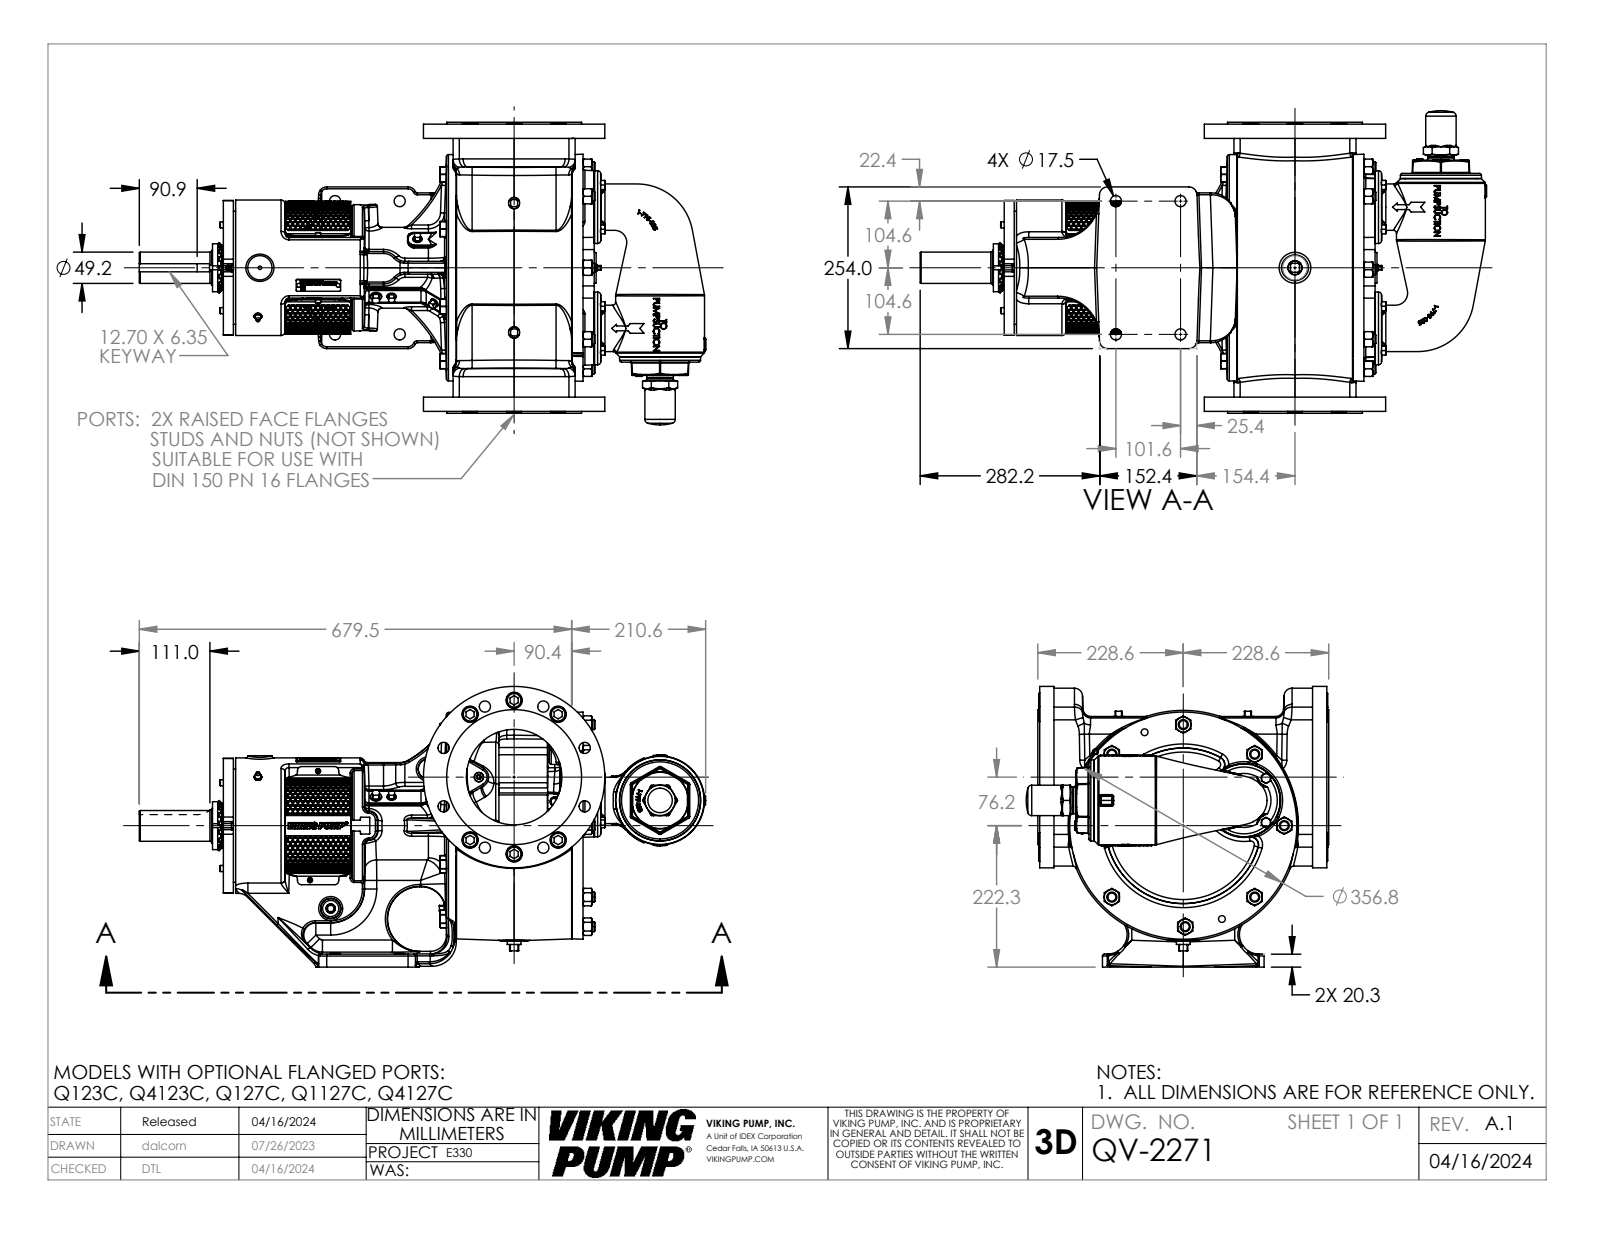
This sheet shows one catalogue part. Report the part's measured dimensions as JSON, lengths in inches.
{"part_name": "QV-2271", "step_written_by": "SolidWorks 2022 (AUTOMOTIVE_DESIGN)", "units": "inches", "bodies": {"solids": 1, "faces": 8750, "planar": 3183, "cylindrical": 833, "other": 4734}, "overall_size": [35.042, 18.719, 17.36], "volume_in3": 2561, "surface_area_in2": 2459, "round_holes": [[0.266, 8], [0.406, 8], [0.689, 8], [1.157, 8], [0.25, 6], [0.656, 6], [1, 6], [0.688, 4], [0.159, 2], [0.313, 2], [0.33, 2], [0.213, 1]], "round_bosses_or_shafts": [[0.375, 10], [0.617, 8], [0.937, 6], [0.625, 4], [0.437, 3], [0.312, 3], [4.5, 2], [0.625, 2]], "partial_cylinders_radius": [[0.12, 60], [0.06, 30], [0.25, 30], [0.5, 23], [0.015, 18], [0.092, 18], [0.75, 14], [0.03, 12]], "face_to_face_distances": [1, 17, 18, 16, 3.75, 0.5, 21.756, 22.256, 18.006, 18.506], "hole_center_spacings": [3.75, 4.724, 2.063, 2.716, 3.133, 3.783, 5.767, 5.932]}
